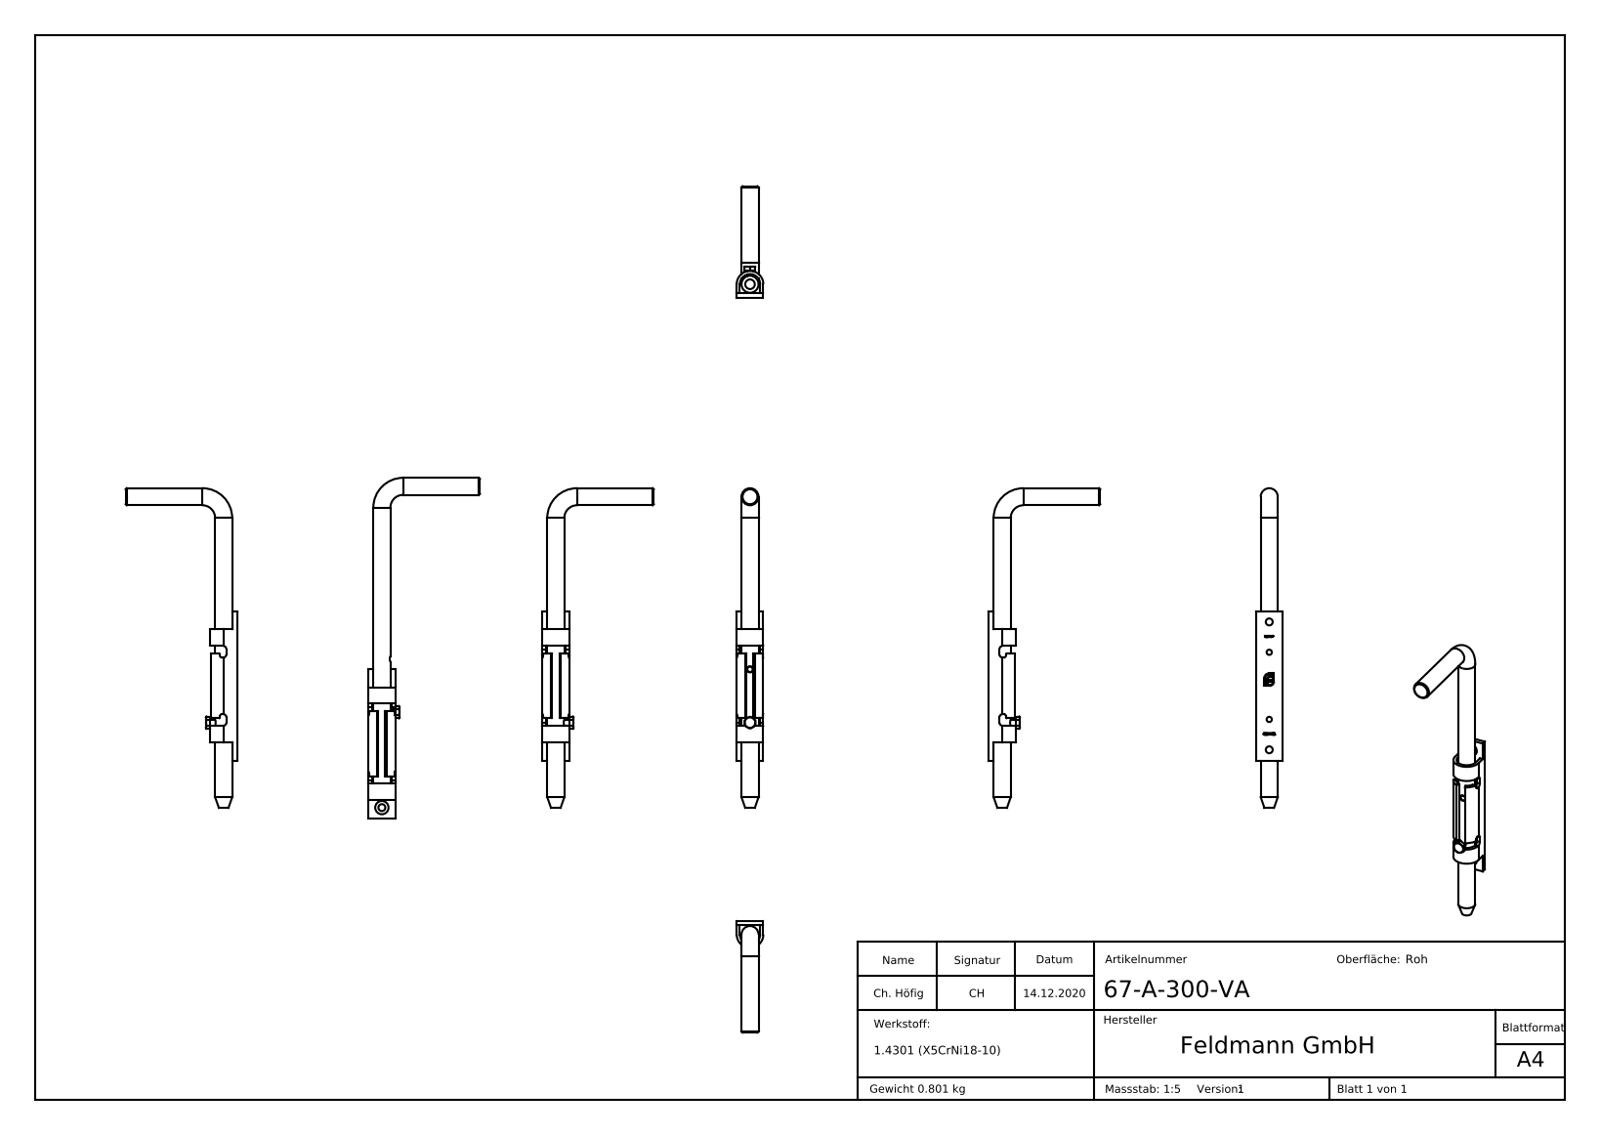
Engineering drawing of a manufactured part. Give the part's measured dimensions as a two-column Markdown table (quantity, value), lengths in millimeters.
| quantity | value |
| --- | --- |
| part name | 67-A-X00 Teil1_67-A-300-VA Teil1; 67-A-X00 Teil1; 67-A-300-VA; DIN 931 (+3 more) |
| STEP written by | SolidWorks 2018 (CONFIG_CONTROL_DESIGN) |
| units | millimeters |
| bodies | 3 solids, 377 faces (196 planar, 42 cylindrical, 139 other) |
| overall size | 300 × 104.5 × 25 |
| volume | 101 400 mm³ |
| surface area | 37 610 mm² |
| round holes (diameter × count) | 4.9 × 2, 5 × 2, 6.5 × 2 |
| round bosses / shafts (diameter × count) | 16 × 2, 6 × 1 |
| partial cylindrical surfaces (radius × count) | 3 × 4, 1 × 2, 2 × 2, 9.5 × 1, 12.5 × 1 |
| main face-to-face distances | 4, 3, 22, 25, 19, 100.5, 15.5, 90.5, 17, 32.5 |
| hole center spacings | 28.5, 91.5, 3, 16, 25.5, 44.5, 47, 50 |
